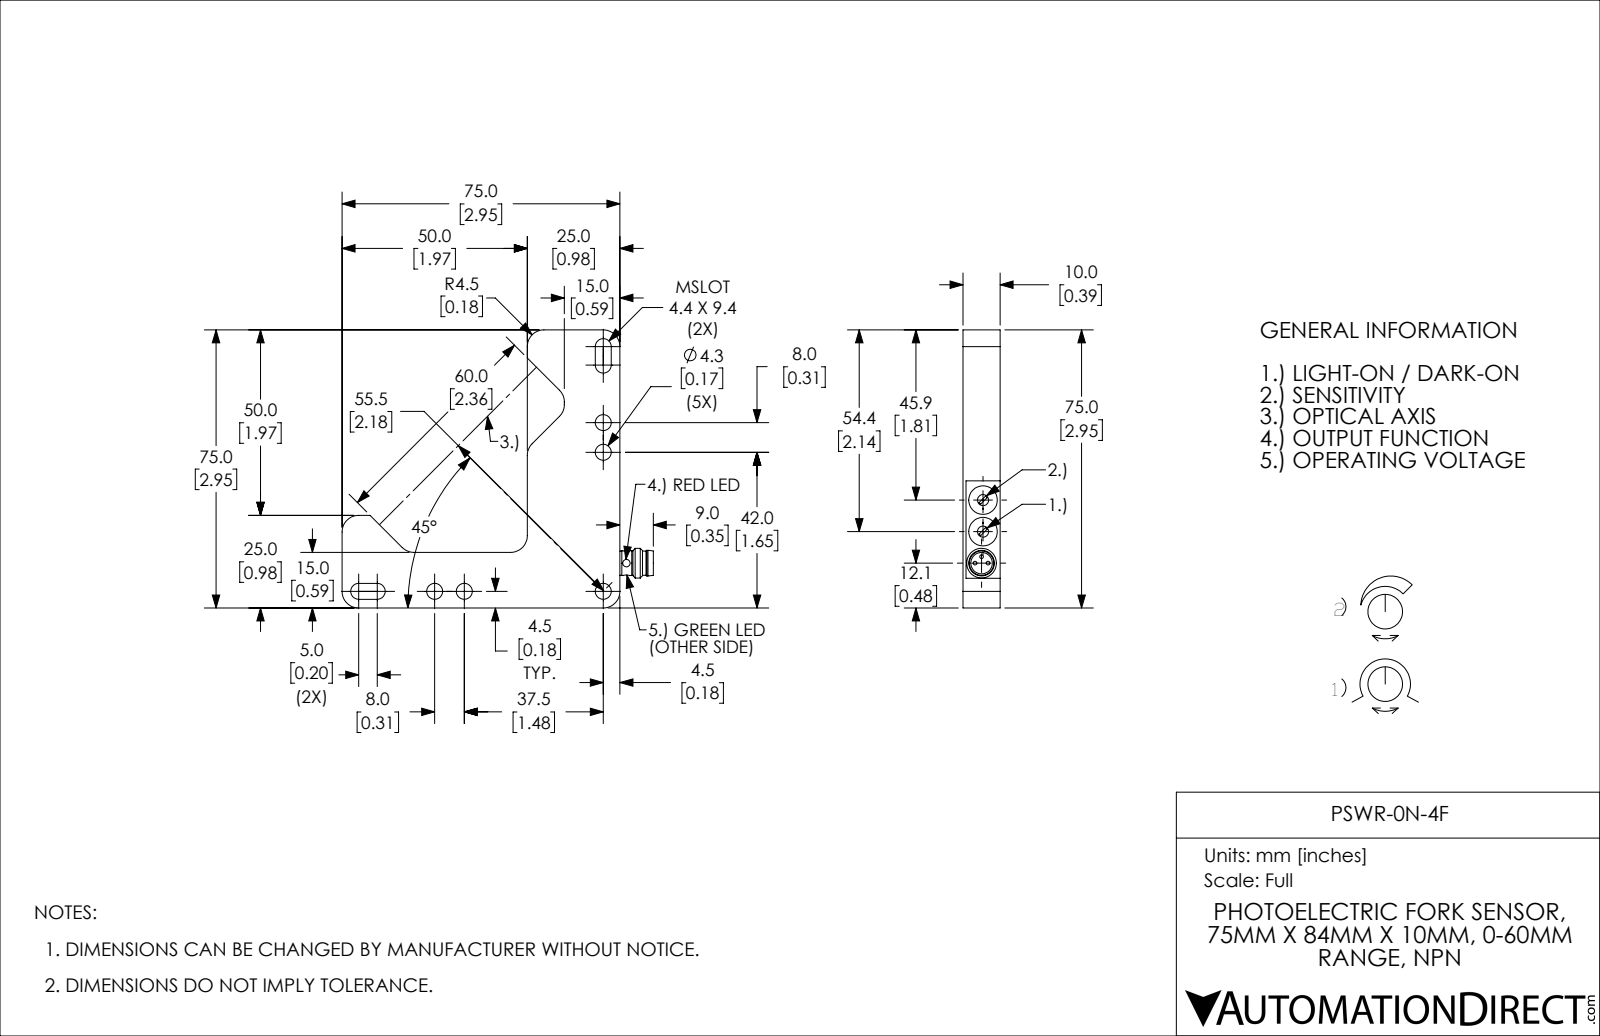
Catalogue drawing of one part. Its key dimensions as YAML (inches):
part_name: "PSWR-0N-4F"
step_written_by: "SolidWorks 2017 (AUTOMOTIVE_DESIGN)"
units: inches
bodies: {solids: 1, faces: 90, planar: 42, cylindrical: 41, other: 7}
overall_size: [3.307, 2.953, 0.394]
volume: 1.504
surface_area: 14.75
round_holes:
  - {diameter: 0.169, count: 5}
  - {diameter: 0.079, count: 2}
  - {diameter: 0.118, count: 2}
  - {diameter: 0.303, count: 2}
  - {diameter: 0.228, count: 1}
round_bosses_or_shafts:
  - {diameter: 0.039, count: 3}
  - {diameter: 0.315, count: 1}
  - {diameter: 0.272, count: 1}
  - {diameter: 0.264, count: 1}
  - {diameter: 0.257, count: 1}
partial_cylinders:
  - {radius: 0.177, count: 10}
  - {radius: 0.085, count: 4}
  - {radius: 0.049, count: 2}
face_to_face_distances: [0.394, 2.953, 2.362, 0.984, 0.591, 1.969, 2.949, 0.98, 0.262, 2.691]
hole_center_spacings: [0.315, 1.476, 1.791, 2.321, 0.335, 0.335, 0.387, 0.669]
